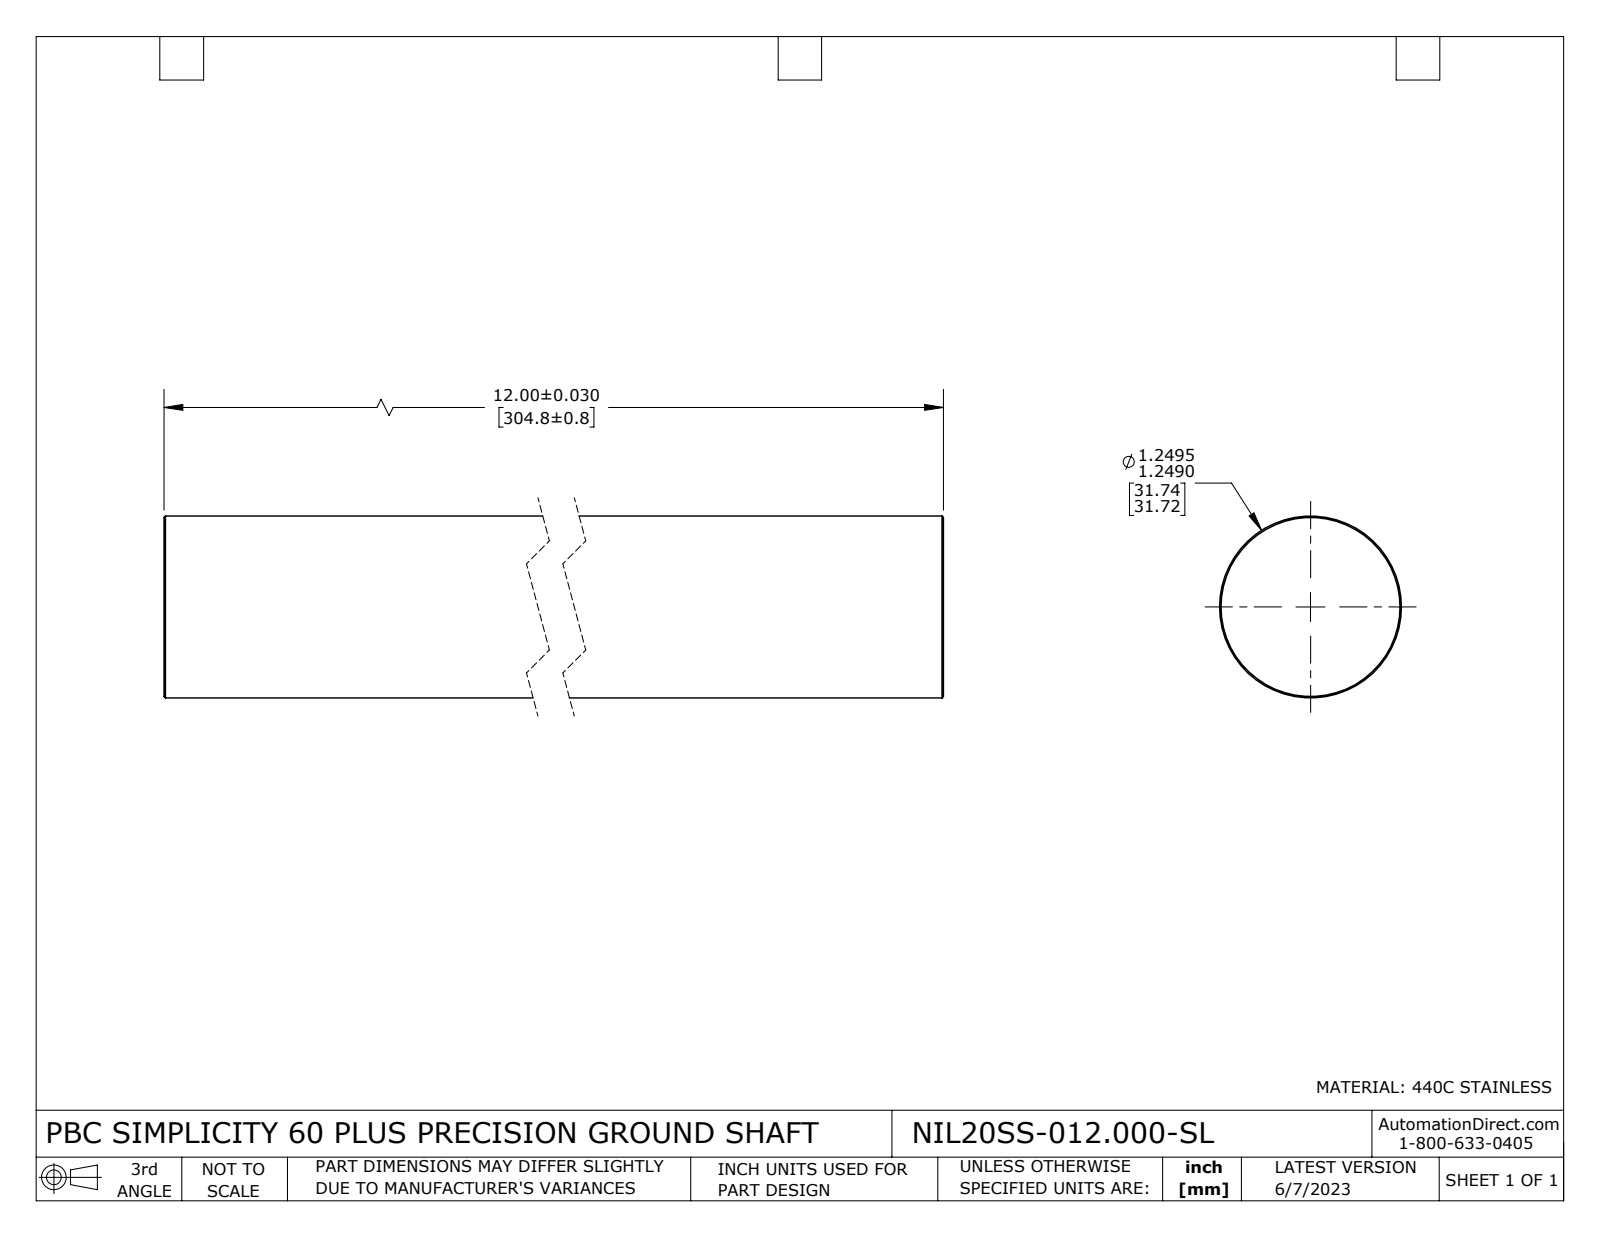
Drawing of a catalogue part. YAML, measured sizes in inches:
part_name: "NIL20SS-012.000-SL"
step_written_by: "SolidWorks 2021 (CONFIG_CONTROL_DESIGN)"
units: inches
bodies: {solids: 1, faces: 8, planar: 2, cylindrical: 2, other: 4}
overall_size: [12, 1.25, 1.25]
volume: 14.73
surface_area: 49.53
round_bosses_or_shafts:
  - {diameter: 1.25, count: 1}
face_to_face_distances: [12]
